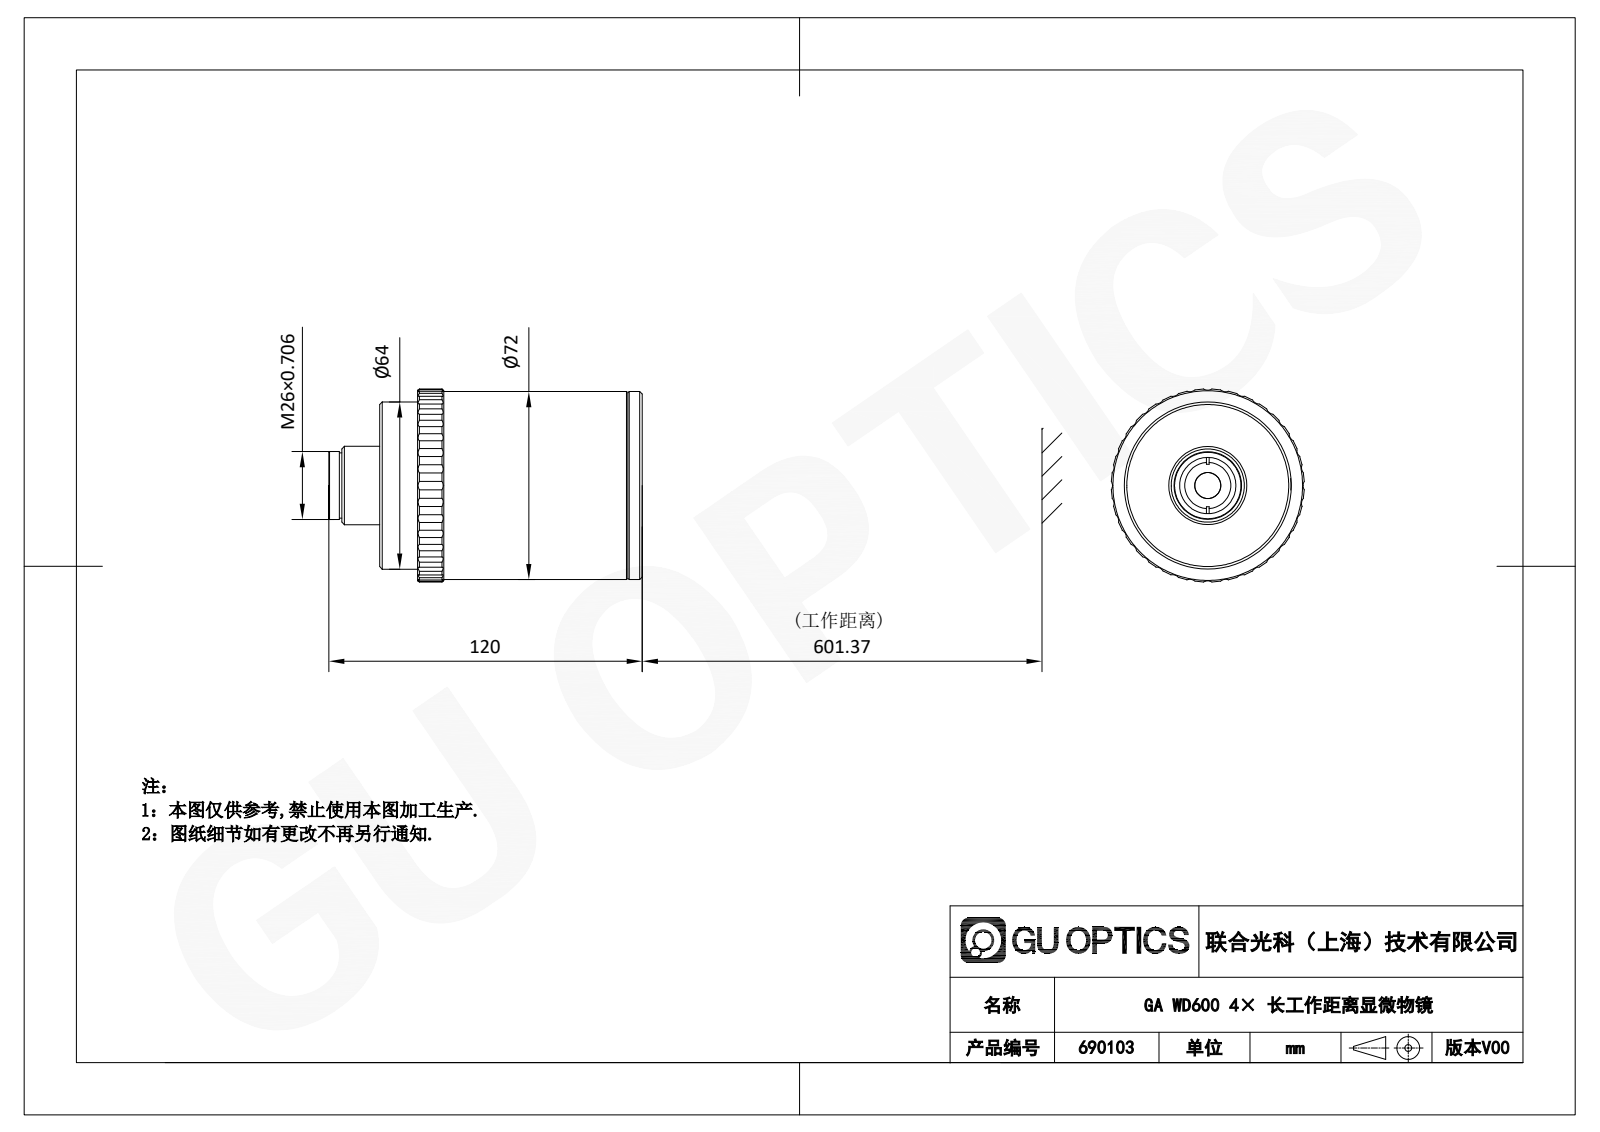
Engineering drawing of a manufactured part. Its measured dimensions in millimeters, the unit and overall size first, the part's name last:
Units: millimetres
Overall size (bounding box): 721.15 × 73.93 × 73.93
Round holes (diameter × count): ⌀21.5 ×1, ⌀62 ×1
Round bosses / shafts (diameter × count): ⌀72 ×1, ⌀66.5 ×1, ⌀64 ×1, ⌀30 ×1, ⌀26 ×1, ⌀25 ×1, ⌀10 ×1
Partial cylindrical surfaces — rounded edges, fillets, slot ends (radius × count): R3 ×36, R36.01 ×1, R37 ×1
Main face-to-face distances: 98.55, 14.5, 84.05, 603.1, 687.15, 701.65, 603, 687.05, 701.55, 601.1
Bodies: 0 solids, 134 faces (15 planar, 105 cylindrical, 14 other)
Part name (STEP PRODUCT): 690103
STEP written by: SolidWorks 2020 (CONFIG_CONTROL_DESIGN)
